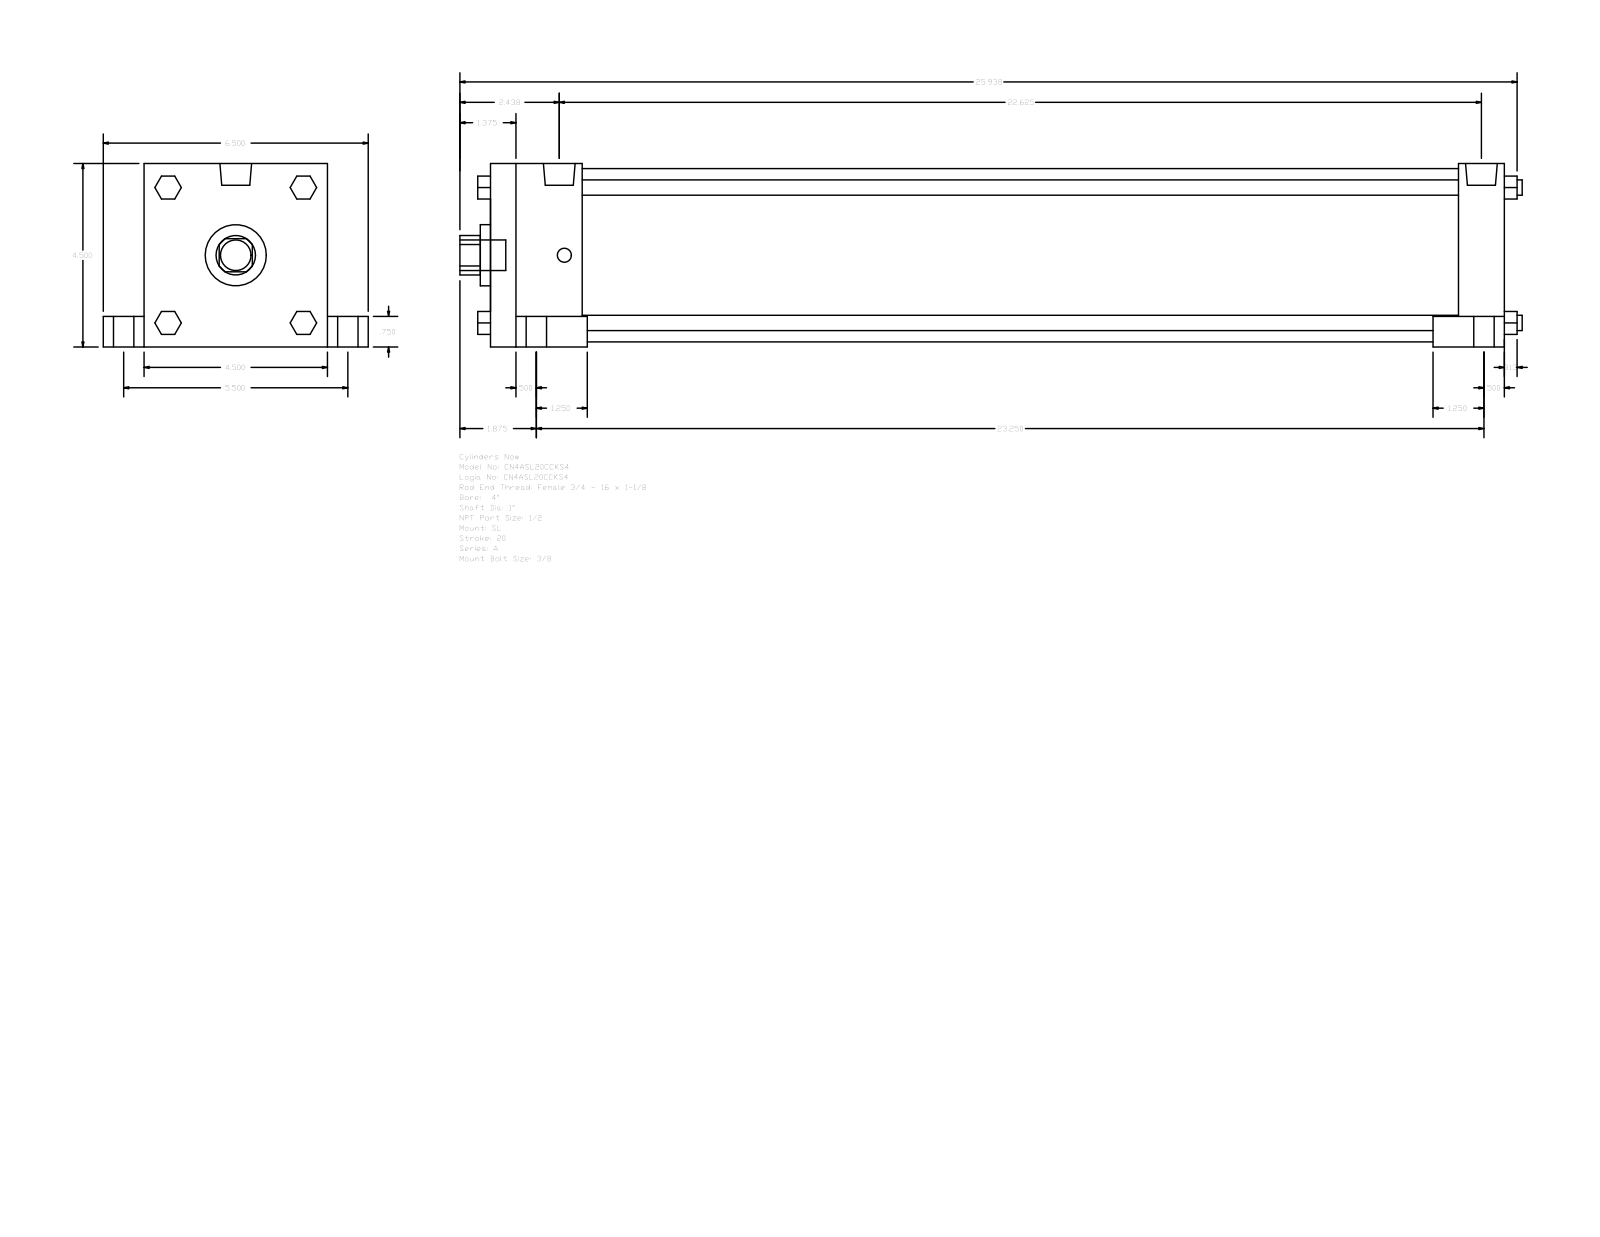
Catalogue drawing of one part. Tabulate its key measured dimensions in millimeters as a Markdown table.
| quantity | value |
| --- | --- |
| part name | A_SL__0400_1 |
| STEP written by | GSSL Pune (CONFIG_CONTROL_DESIGN) |
| units | millimeters |
| bodies | 0 solids, 150 faces (114 planar, 36 cylindrical, 0 other) |
| overall size | 661.99 × 165.1 × 114.3 |
| round holes (diameter × count) | 25.4 × 1, 38.1 × 1, 107.95 × 1 |
| round bosses / shafts (diameter × count) | 19.05 × 5, 12.7 × 4, 9.53 × 4, 8.73 × 4, 19.77 × 2 |
| partial cylindrical surfaces (radius × count) | 12.29 × 1 |
| main face-to-face distances | 114.3, 631.83, 57.15, 574.68, 603.25, 546.1, 28.58, 19.05, 25.4, 139.7 |
